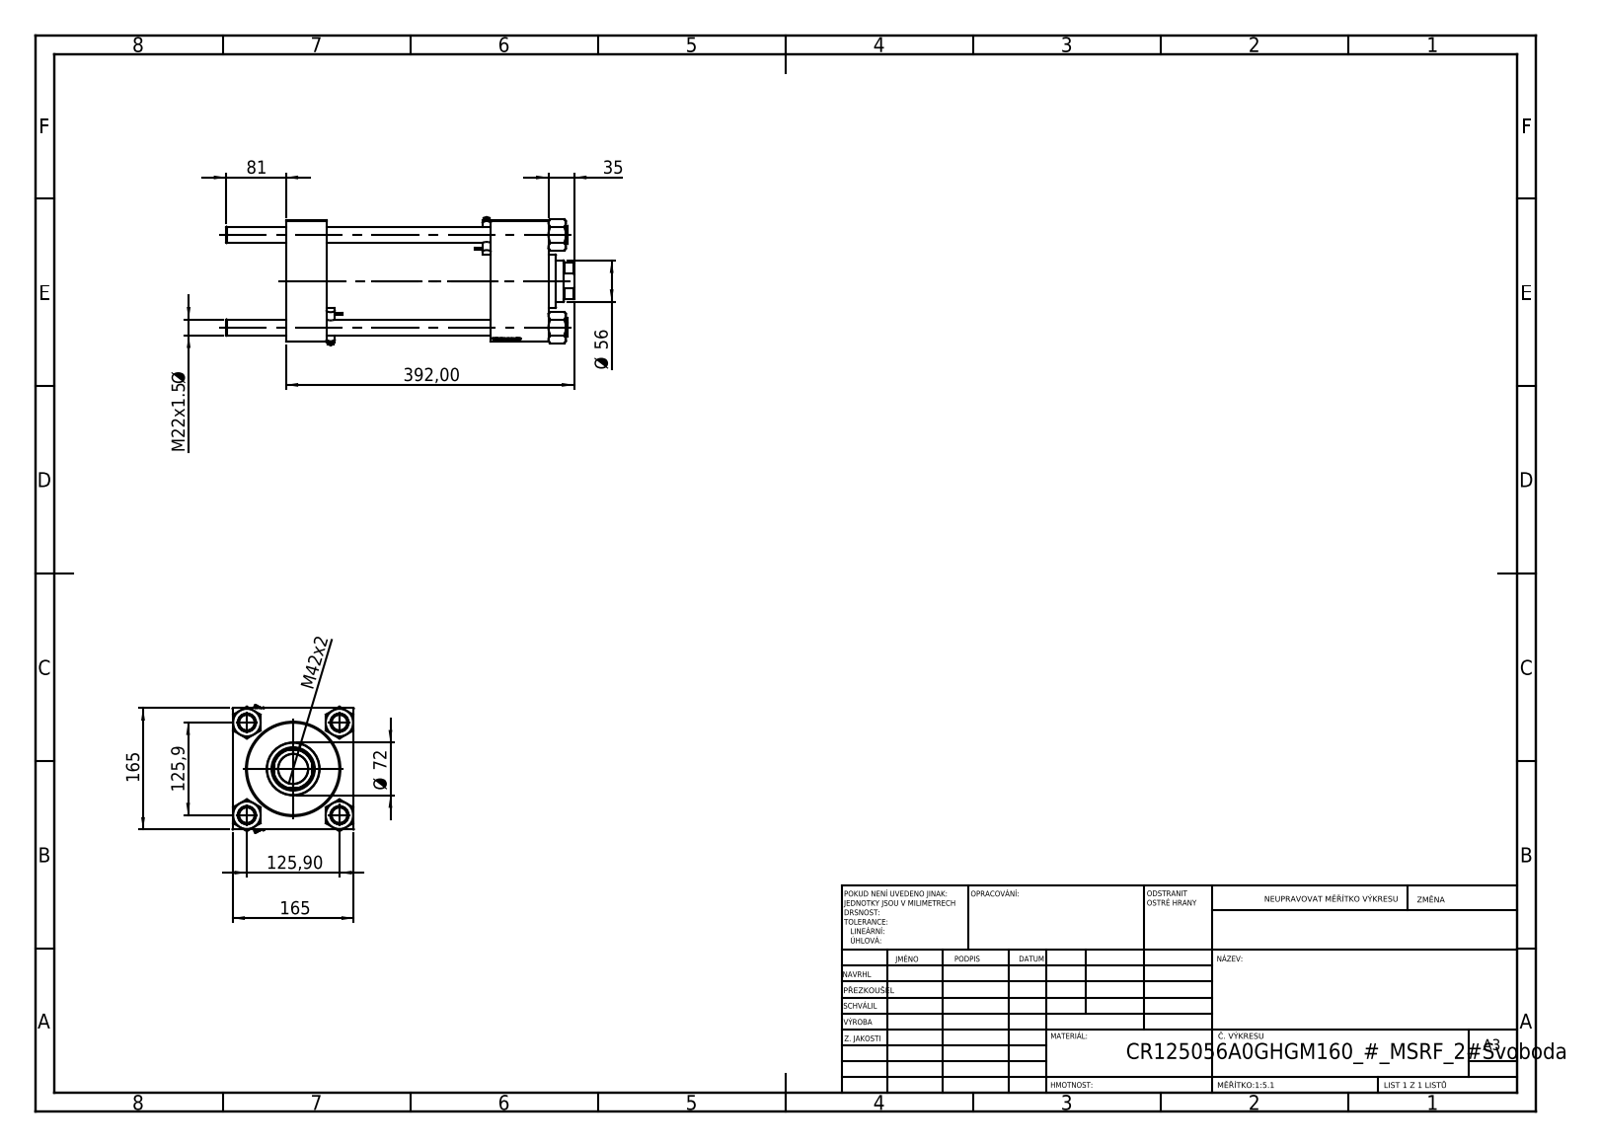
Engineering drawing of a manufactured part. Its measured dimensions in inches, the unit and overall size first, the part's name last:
Units: inches
Overall size (bounding box): 18.622 × 6.844 × 6.496
Round holes (diameter × count): ⌀0.866 ×4, ⌀0.276 ×2, ⌀1.269 ×2, ⌀1.772 ×2, ⌀1.594 ×1, ⌀2.205 ×1, ⌀2.323 ×1, ⌀3.78 ×1, ⌀4.921 ×1, ⌀4.941 ×1
Round bosses / shafts (diameter × count): ⌀0.984 ×4, ⌀0.197 ×2, ⌀0.098 ×2, ⌀5.157 ×1, ⌀2.835 ×1
Partial cylindrical surfaces — rounded edges, fillets, slot ends (radius × count): R0.02 ×12, R0.236 ×4, R1.063 ×1
Main face-to-face distances: 6.496, 2.165, 14.055, 11.89, 10.984, 8.819, 3.071, 12.925, 10.76, 1.941
Hole centre spacings: 3.505, 4.957, 7.01, 10.965
Volume: 330.5 in³ · Surface area: 1 131 in²
Bodies: 13 solids, 1246 faces (604 planar, 106 cylindrical, 536 other)
Part name (STEP PRODUCT): CR025_012_A_0_G_A_G_M_020_+#_##_TYCINKA; V215_VC_A; NUT_M5; V215CR_VCP (+2 more)
STEP written by: SolidWorks 2019 (CONFIG_CONTROL_DESIGN)
